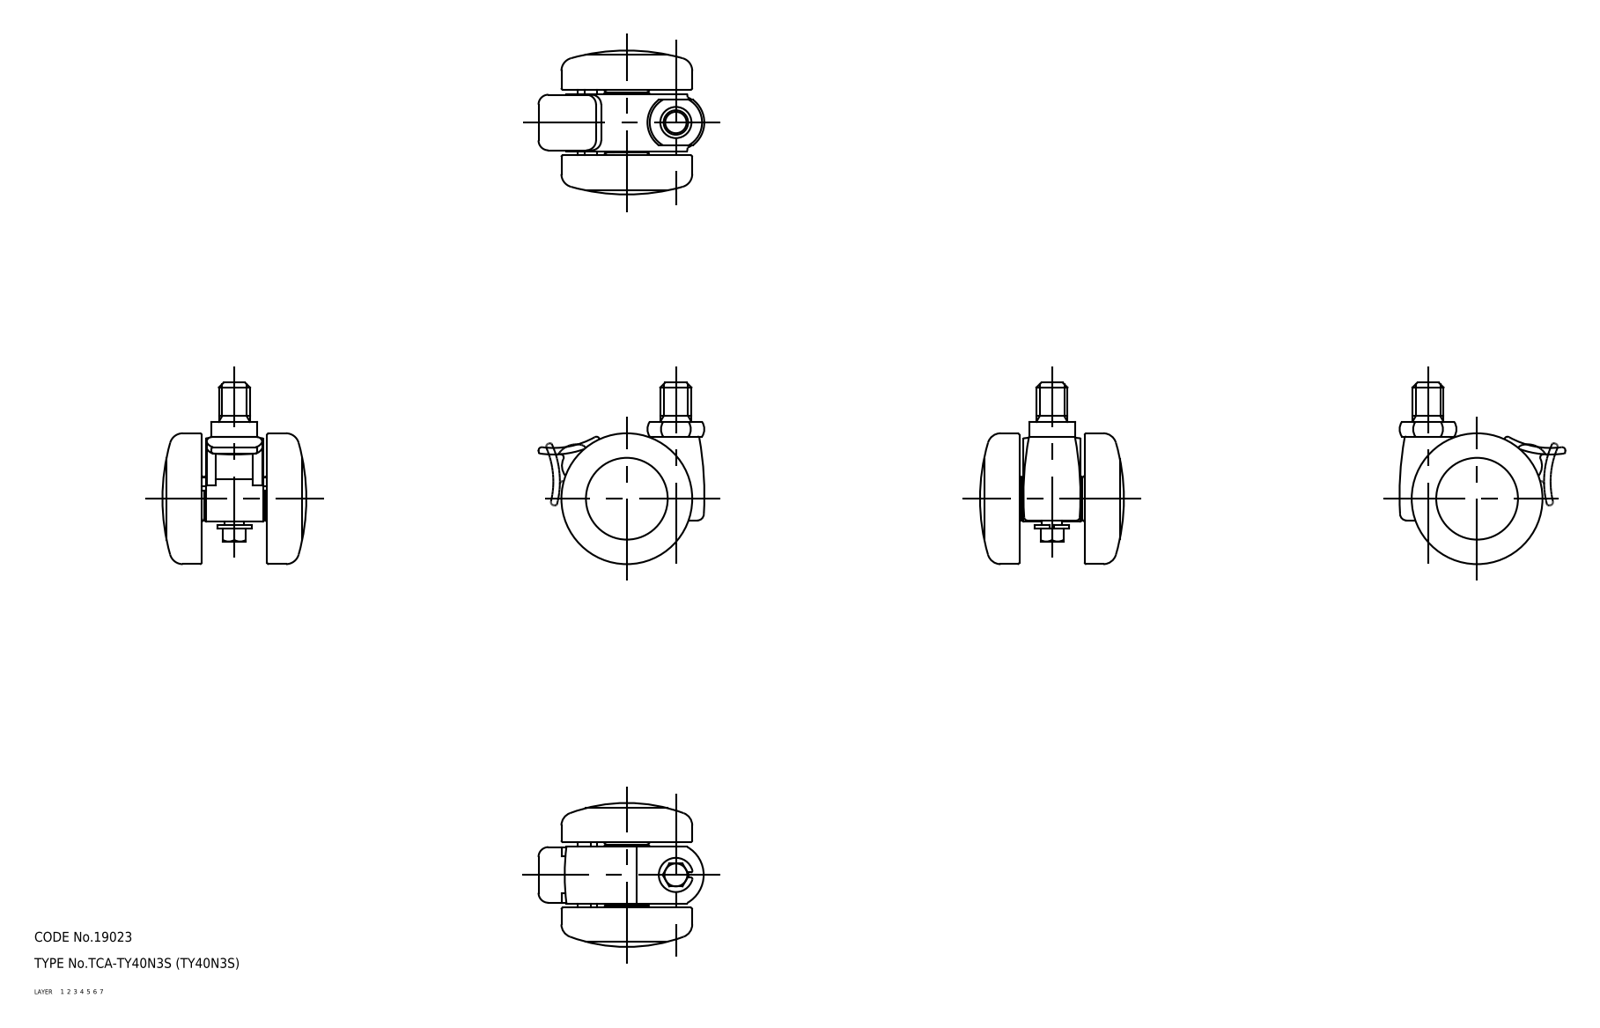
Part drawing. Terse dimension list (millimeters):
name: wheel; main shaft; lever; TY40N3S_10482_36
written by: CADfix (AUTOMOTIVE_DESIGN)
unit: mm
bodies: 5 solids, 193 faces (0 planar, 0 cylindrical, 193 other)
size: 55.5 × 50.72 × 44
volume: 39 738 mm³; area: 19 087 mm²
